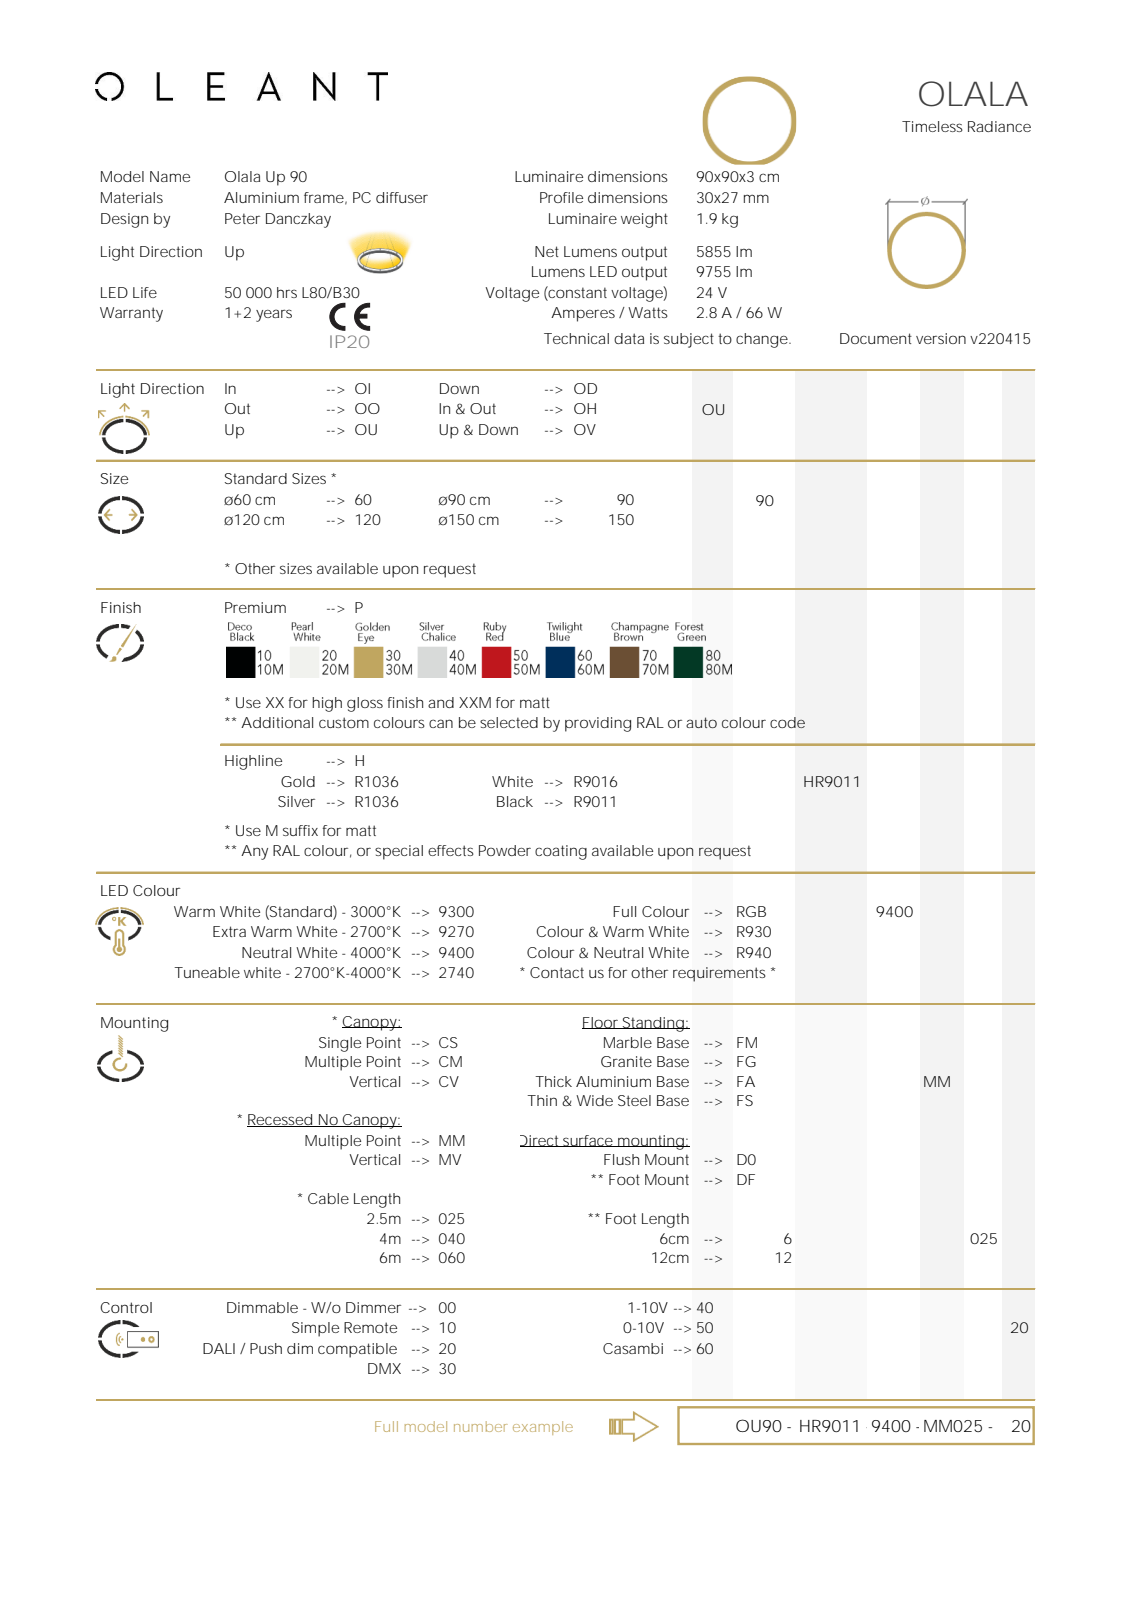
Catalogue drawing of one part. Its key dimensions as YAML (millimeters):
part_name: "olala; frame; plexi; cable (+1 more)"
step_written_by: "Autodesk Inventor 2020 (AUTOMOTIVE_DESIGN)"
units: millimeters
bodies: {solids: 8, faces: 84, planar: 43, cylindrical: 31, other: 10}
overall_size: [1049.5, 900, 900]
volume: 2146000
surface_area: 728153
round_holes:
  - {diameter: 3, count: 3}
  - {diameter: 840, count: 1}
  - {diameter: 896, count: 1}
round_bosses_or_shafts:
  - {diameter: 11, count: 3}
  - {diameter: 9, count: 3}
  - {diameter: 4, count: 3}
  - {diameter: 1.2, count: 3}
  - {diameter: 900, count: 1}
  - {diameter: 898, count: 1}
  - {diameter: 844, count: 1}
face_to_face_distances: [2, 24.5, 22.5, 26.5, 12, 11.98, 12.02, 1049.5, 1047.5, 1025]
hole_center_spacings: [435, 753.44]
